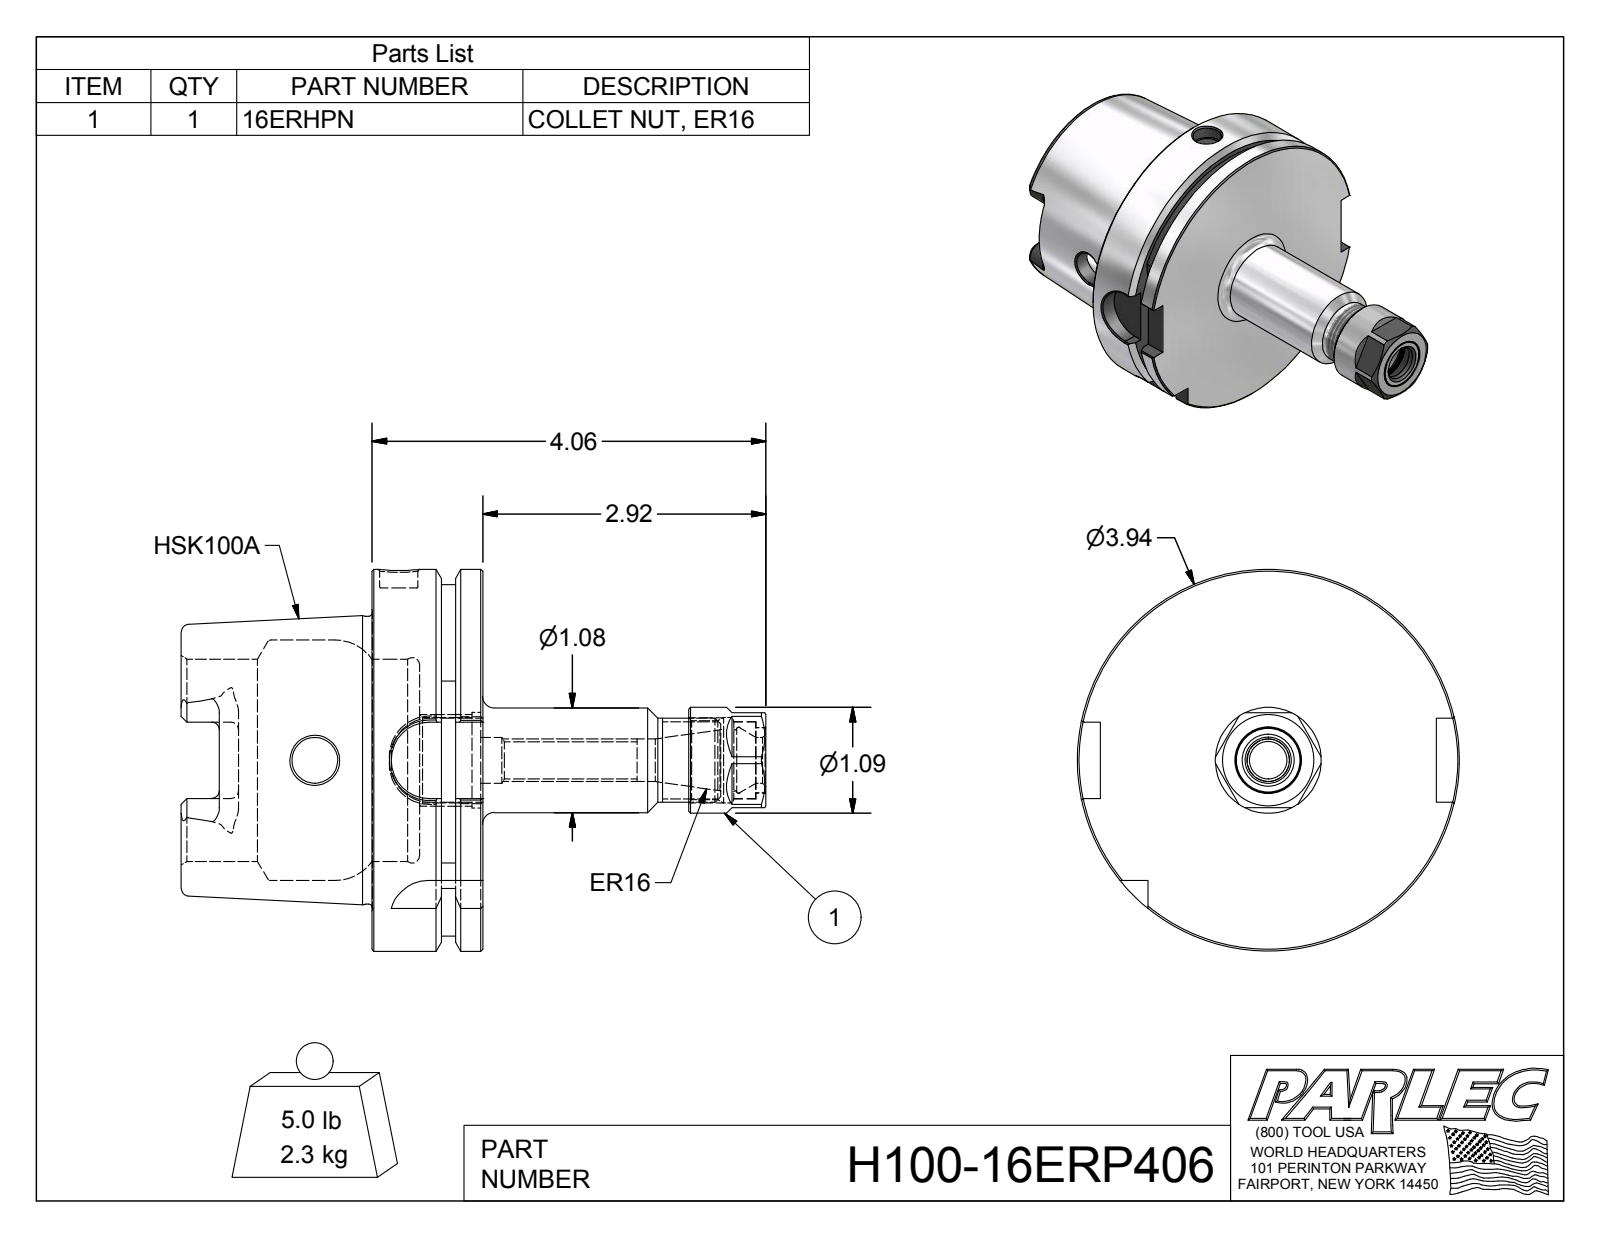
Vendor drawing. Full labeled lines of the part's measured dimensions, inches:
Part name (STEP PRODUCT): H100-16ERP406; H100-16ER4-1; 16ERHPN
STEP written by: Autodesk Inventor 2012 (AUTOMOTIVE_DESIGN)
Units: inches
Bodies: 3 solids, 173 faces (64 planar, 46 cylindrical, 63 other)
Overall size (bounding box): 6.029 × 3.937 × 3.937
Volume: 17.49 in³ · Surface area: 95.6 in²
Round holes (diameter × count): ⌀0.472 ×2, ⌀0.383 ×1, ⌀0.394 ×1, ⌀0.44 ×1, ⌀0.472 ×1, ⌀0.474 ×1, ⌀0.63 ×1, ⌀0.674 ×1, ⌀0.68 ×1, ⌀0.794 ×1, ⌀0.814 ×1, ⌀0.881 ×1
Round bosses / shafts (diameter × count): ⌀3.937 ×1, ⌀2.967 ×1, ⌀1.092 ×1, ⌀1.08 ×1, ⌀0.866 ×1, ⌀0.79 ×1, ⌀0.67 ×1
Partial cylindrical surfaces — rounded edges, fillets, slot ends (radius × count): R0.079 ×6, R0.192 ×4, R0.394 ×4, R1.811 ×1
Main face-to-face distances: 1.142, 0.492, 0.65, 1.969, 2.461, 3.11, 2.83, 0.861, 0.369, 0.28
